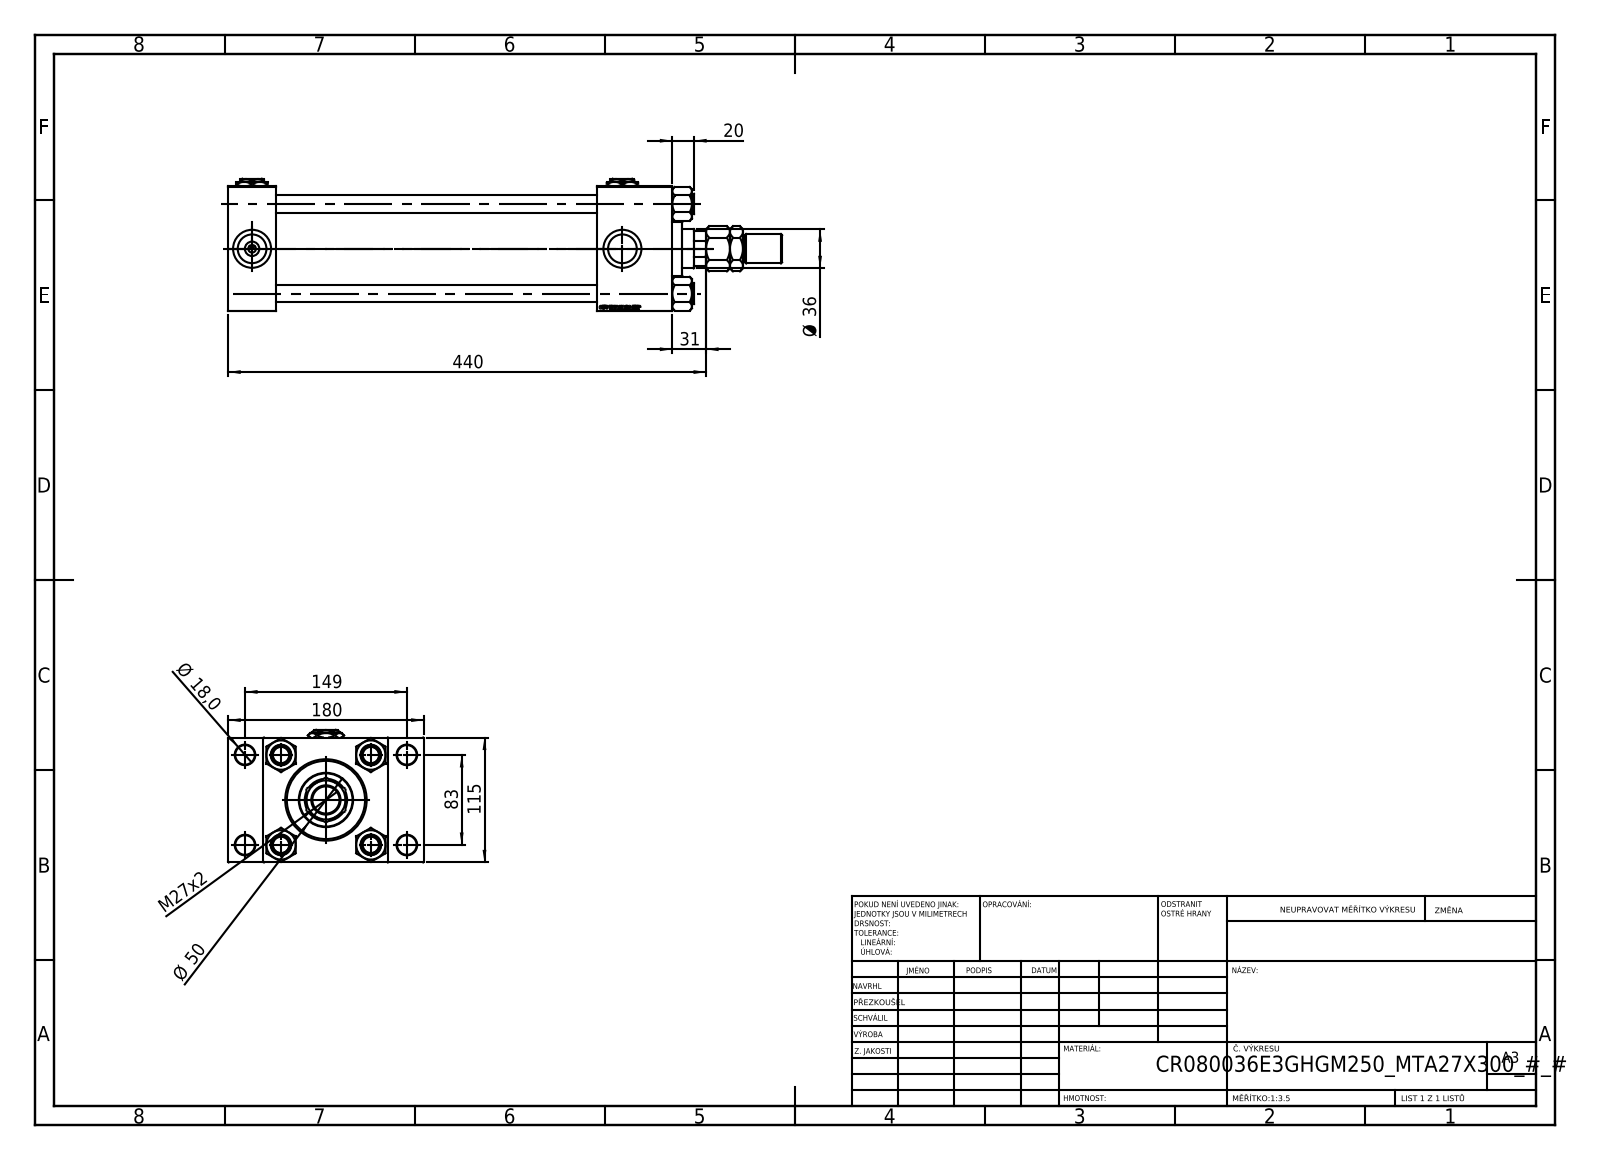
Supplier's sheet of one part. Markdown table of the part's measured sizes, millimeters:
| quantity | value |
| --- | --- |
| part name | V215CR_TYCINKA_E; NUT_M5_E; V215CR_E_Body; V215_VC_A (+3 more) |
| STEP written by | SolidWorks 2019 (CONFIG_CONTROL_DESIGN) |
| units | millimeters |
| bodies | 14 solids, 1333 faces (608 planar, 101 cylindrical, 624 other) |
| overall size | 510 × 180 × 122 |
| volume | 2 727 000 mm³ |
| surface area | 518 981 mm² |
| round holes (diameter × count) | 16 × 4, 18 × 4, 26.44 × 4, 35 × 4, 7 × 3, 25.5 × 1, 36 × 1, 39 × 1, 61 × 1, 72 × 1, 80 × 1 |
| round bosses / shafts (diameter × count) | 19 × 4, 86 × 1, 50 × 1, 27 × 1, 25 × 1 |
| partial cylindrical surfaces (radius × count) | 17.5 × 1 |
| main face-to-face distances | 115, 44, 409, 365, 32.5, 147.5, 69, 340, 296, 380.3 |
| hole center spacings | 33.15, 58.48, 82.7, 85.28, 89.24, 115.85, 142.43, 83 |
